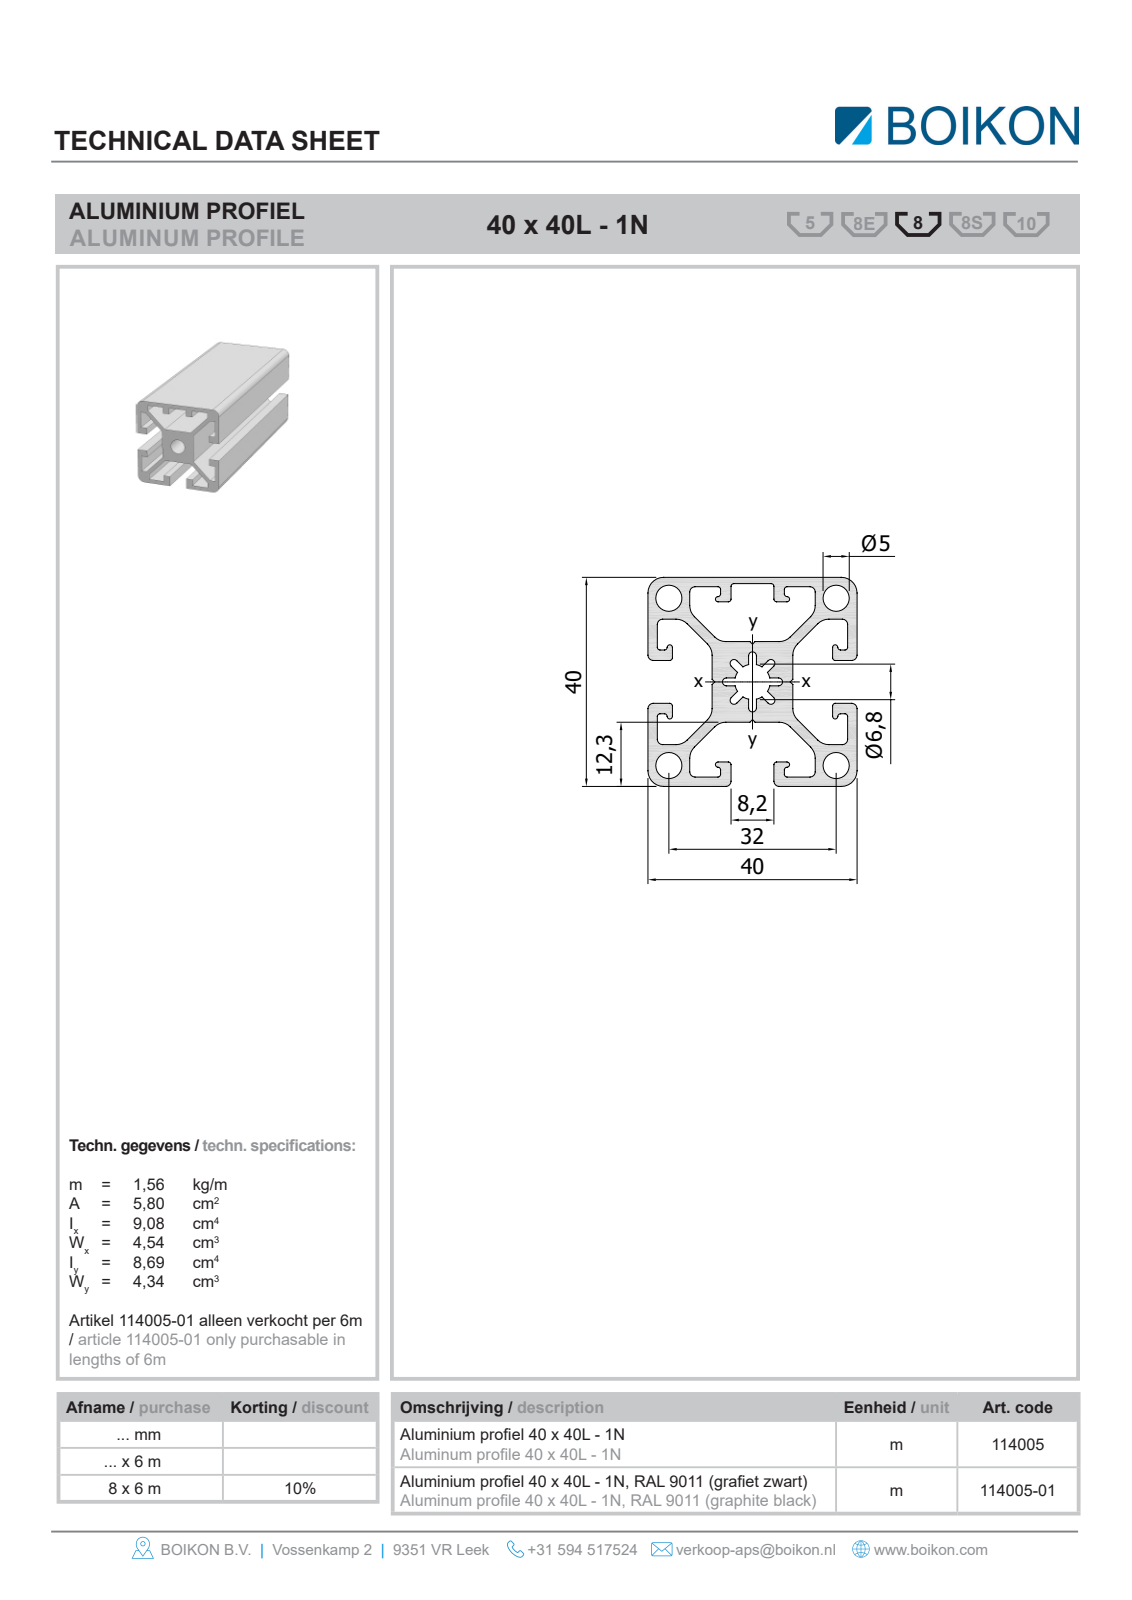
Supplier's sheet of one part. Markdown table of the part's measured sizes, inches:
| quantity | value |
| --- | --- |
| part name | Root; 11400540x40L-1NBOIKON0 |
| STEP written by | HiCAD 2013 1802.4 Build 509 (AUTOMOTIVE_DESIGN) |
| units | inches |
| bodies | 1 solid, 67 faces (62 planar, 5 cylindrical, 0 other) |
| overall size | 39.37 × 1.575 × 1.575 |
| volume | 37.76 in³ |
| surface area | 719.1 in² |
| round holes (diameter × count) | 0.268 × 1 |
| partial cylindrical surfaces (radius × count) | 0.118 × 4 |
| main face-to-face distances | 0.071, 1.504, 1.575, 0.488, 0.417, 1.087, 1.016, 0.441, 0.323, 0.626 |
